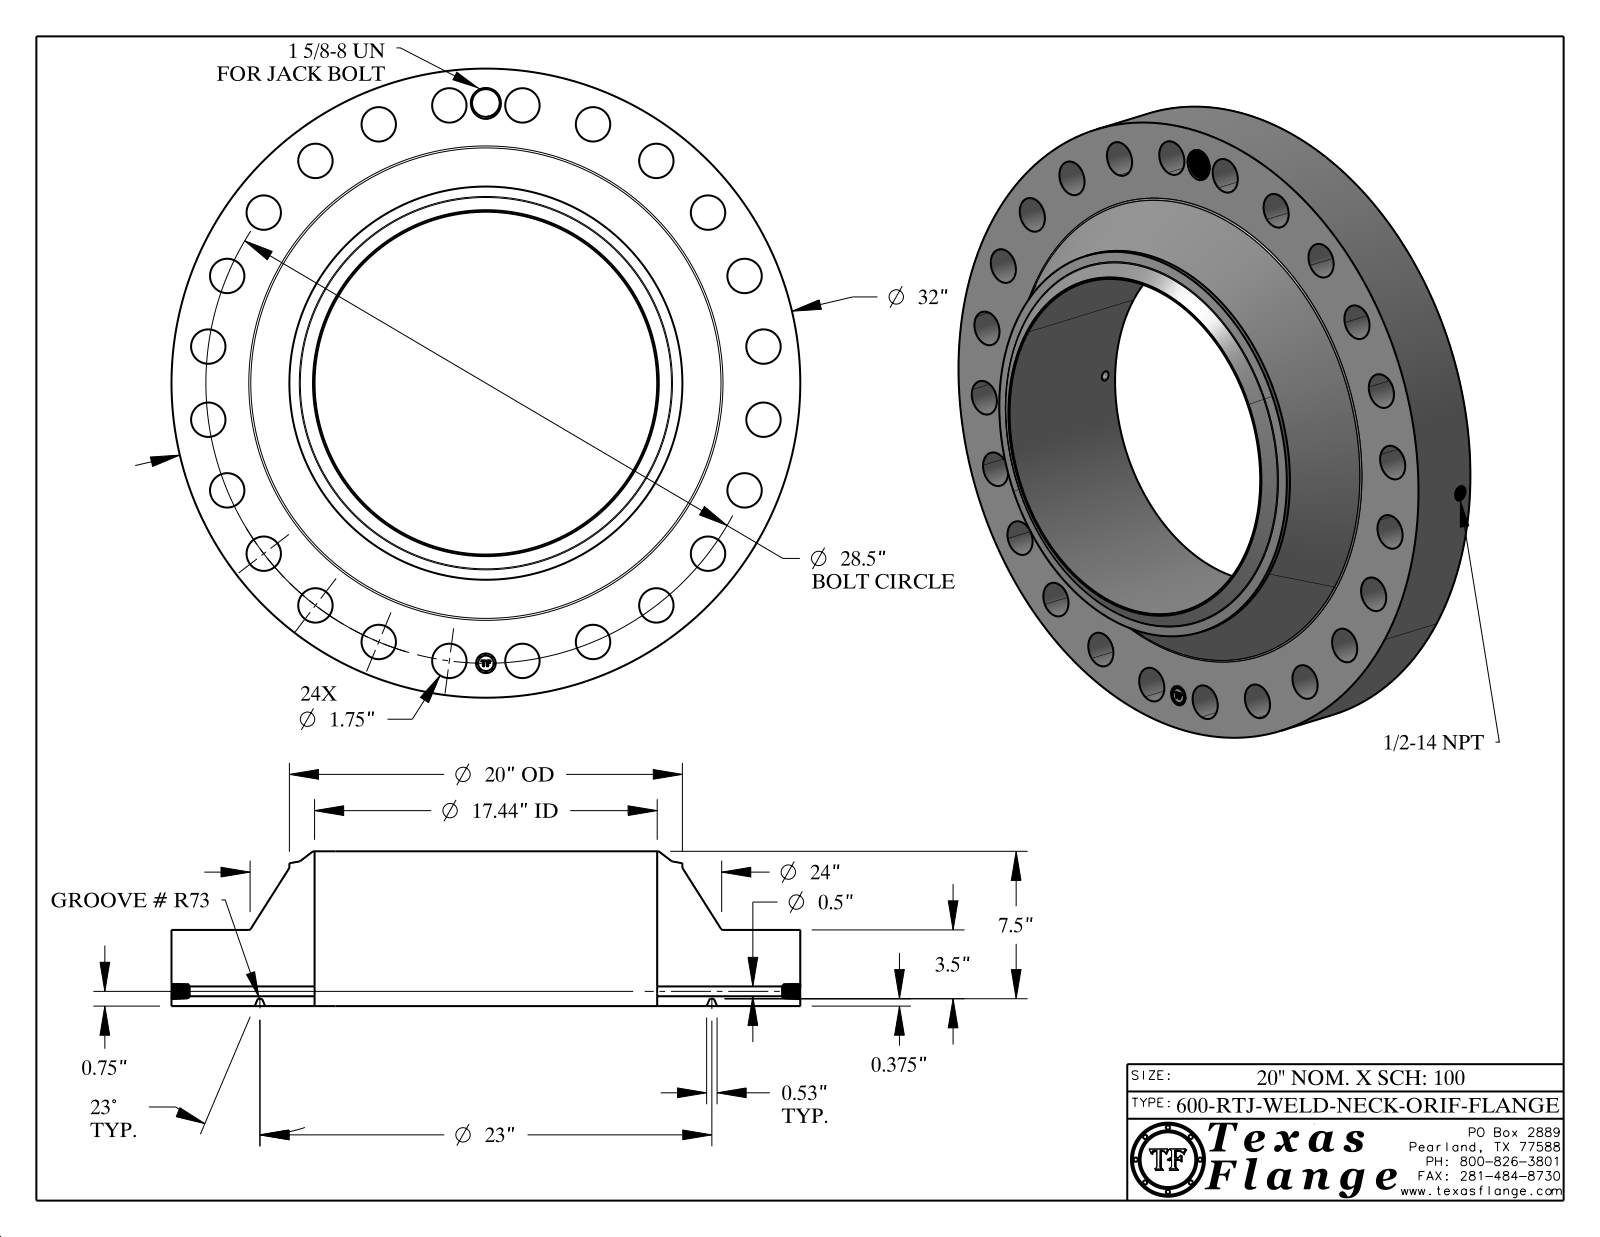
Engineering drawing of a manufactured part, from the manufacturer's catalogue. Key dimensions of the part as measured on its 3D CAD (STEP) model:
Part name (STEP PRODUCT): 600-RTJ-WELD-NECK
STEP written by: CATIA V5 STEP AP214 (AUTOMOTIVE_DESIGN)
Units: inches
Bodies: 1 solid, 908 faces (370 planar, 155 cylindrical, 383 other)
Overall size (bounding box): 32 × 32 × 7.875
Volume: 2 432 in³ · Surface area: 2 586 in²
Round holes (diameter × count): ⌀1.75 ×24, ⌀0.5 ×1, ⌀0.672 ×1, ⌀1 ×1, ⌀1.409 ×1, ⌀17.438 ×1
Round bosses / shafts (diameter × count): ⌀0.061 ×8, ⌀32 ×1, ⌀20 ×1, ⌀0.788 ×1
Main face-to-face distances: 3.875, 0.375, 3.5, 7.875, 7.5, 4, 0.015, 3.86, 3.485, 4.015
Hole centre spacings: 14.25, 17.35, 24.681, 28.256, 10.906, 3.72, 7.376, 20.152
